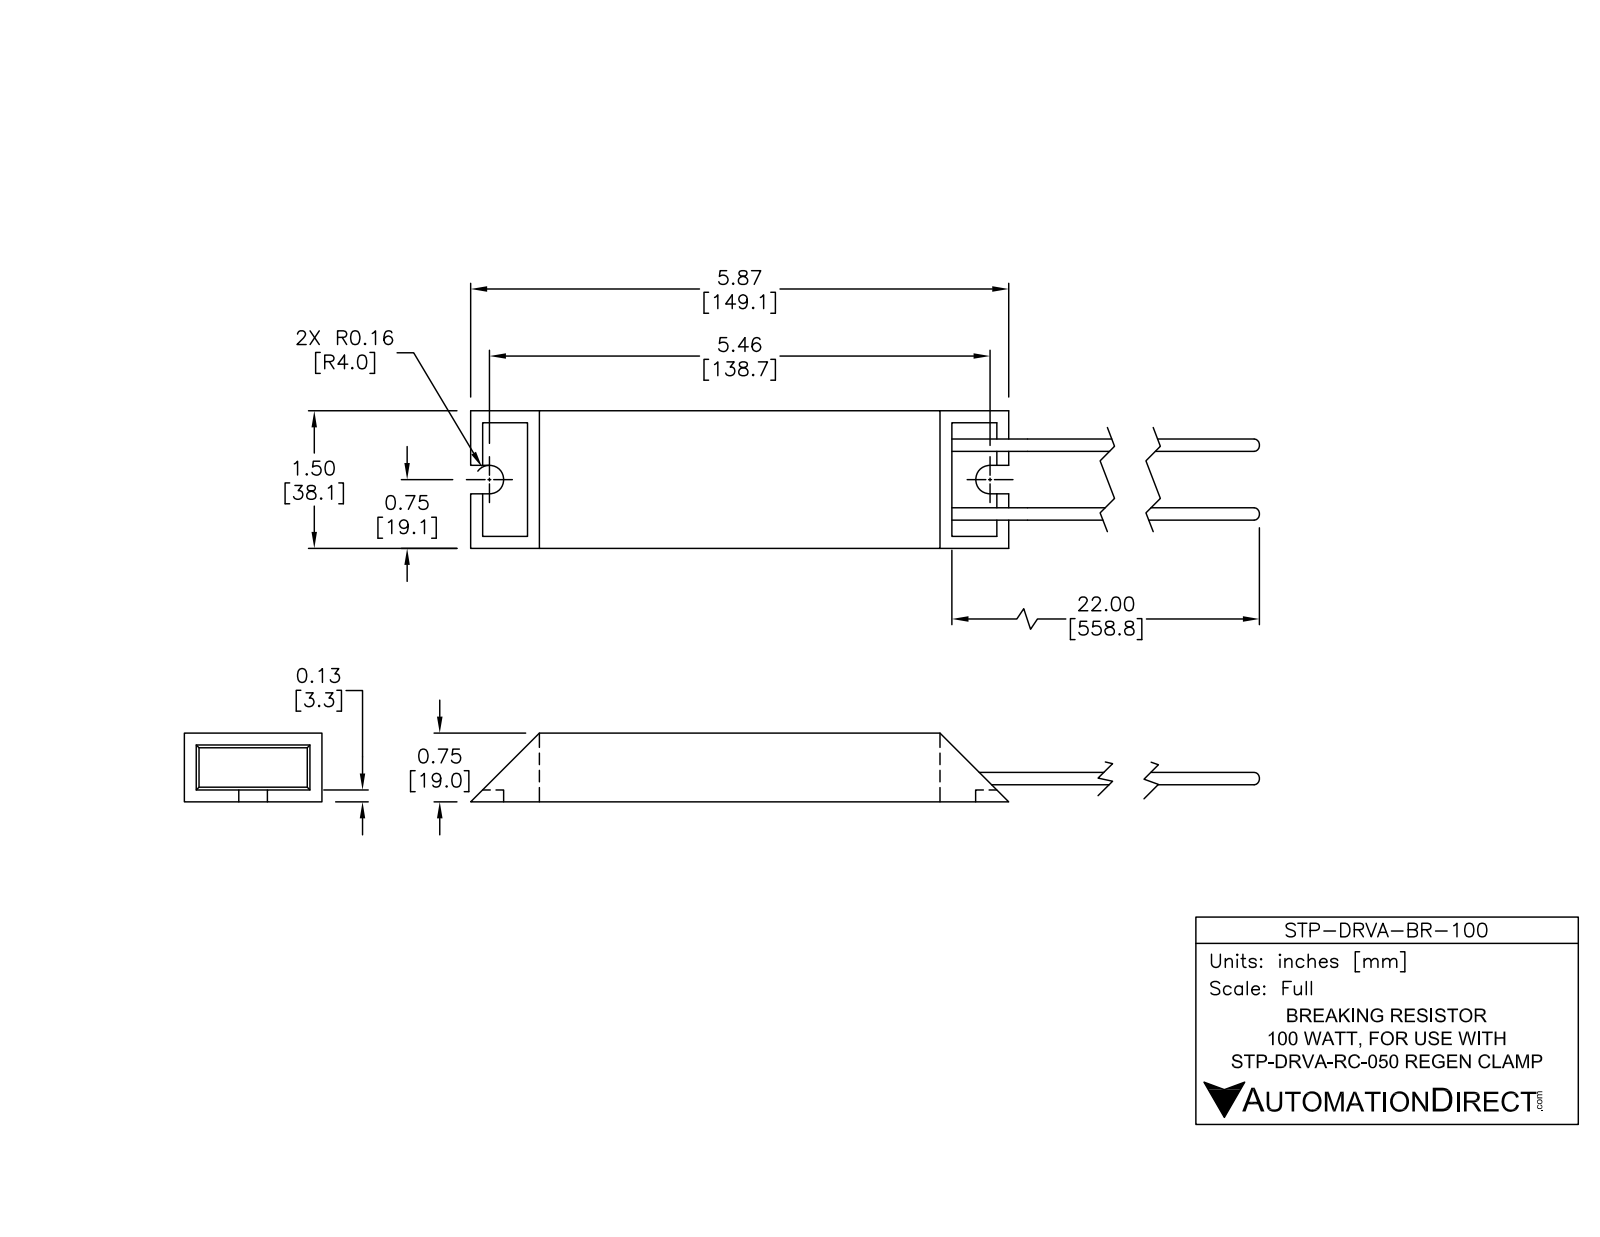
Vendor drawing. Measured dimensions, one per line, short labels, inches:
name: STP-DRVA-BR-100
written by: SolidWorks 2013 (AUTOMOTIVE_DESIGN)
unit: in
bodies: 1 solid, 40 faces (22 planar, 14 cylindrical, 4 other)
size: 11.204 × 2.432 × 1.5
volume: 5.575 in³; area: 32.96 in²
bosses: 1× ⌀0.135, 1× ⌀0.135
rounds: 8× R0.03, 2× R0.156
face distances: 0.75, 1.5, 0.13, 0.62, 1.37, 4.54, 1.24, 0.594, 0.906, 0.464
